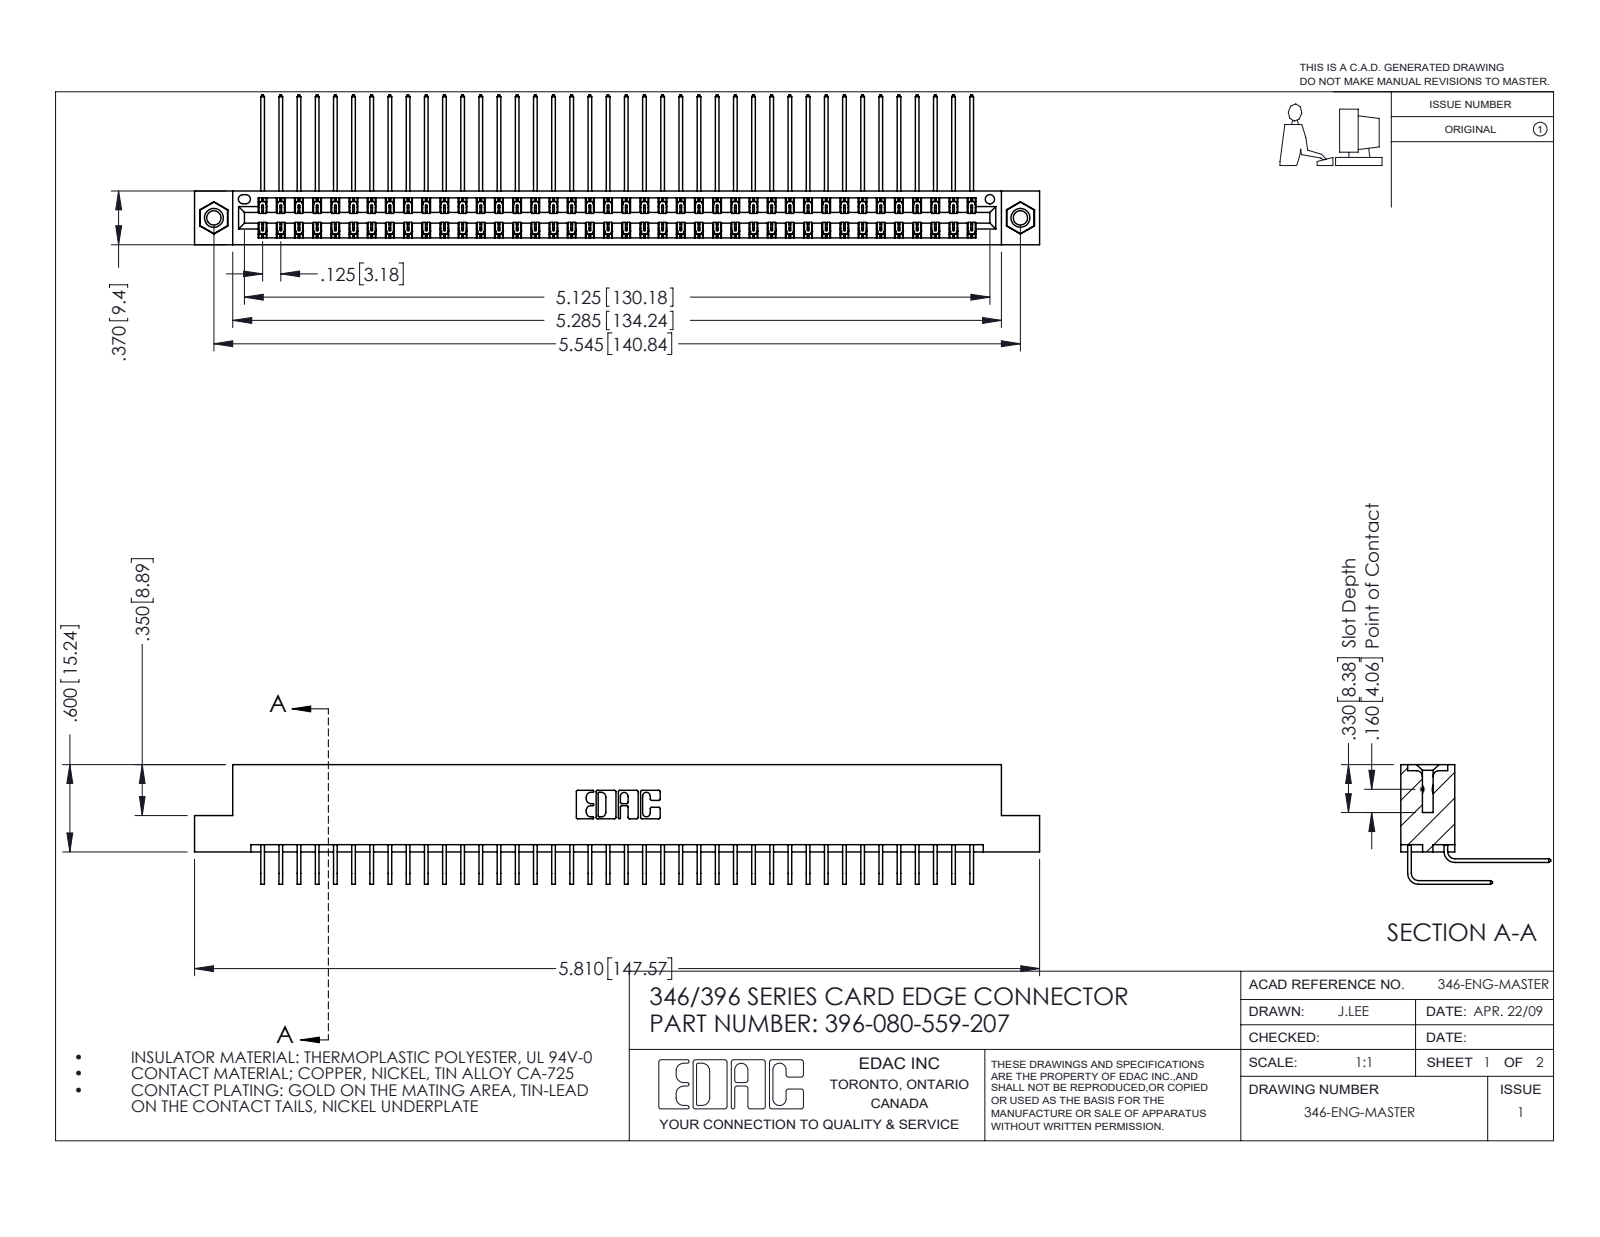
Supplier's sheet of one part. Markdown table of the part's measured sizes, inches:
| quantity | value |
| --- | --- |
| part name | 345-292-001_558 559 Tail - 1; 345-250-001_345-250-005-103; 396-080-559-207; 345-292-001_559 Tail - 2 (+1 more) |
| STEP written by | SolidWorks 2016 (CONFIG_CONTROL_DESIGN) |
| units | inches |
| bodies | 83 solids, 4502 faces (3068 planar, 1418 cylindrical, 16 other) |
| overall size | 5.81 × 1.03 × 0.823 |
| volume | 0.905 in³ |
| surface area | 35.02 in² |
| round holes (diameter × count) | 0.098 × 2, 0.125 × 2, 0.156 × 2, 0.064 × 1 |
| round bosses / shafts (diameter × count) | 0.155 × 2 |
| partial cylindrical surfaces (radius × count) | 0.006 × 120, 0.01 × 22, 0.007 × 6, 0.031 × 6, 0.026 × 3, 0.014 × 2, 0.022 × 2, 0.024 × 2 |
| main face-to-face distances | 0.048, 0.322, 0.025, 0.37, 0.25, 0.072, 0.298, 0.275, 0.148, 0.222 |
| hole center spacings | 0.246, 5.336, 5.545 |
